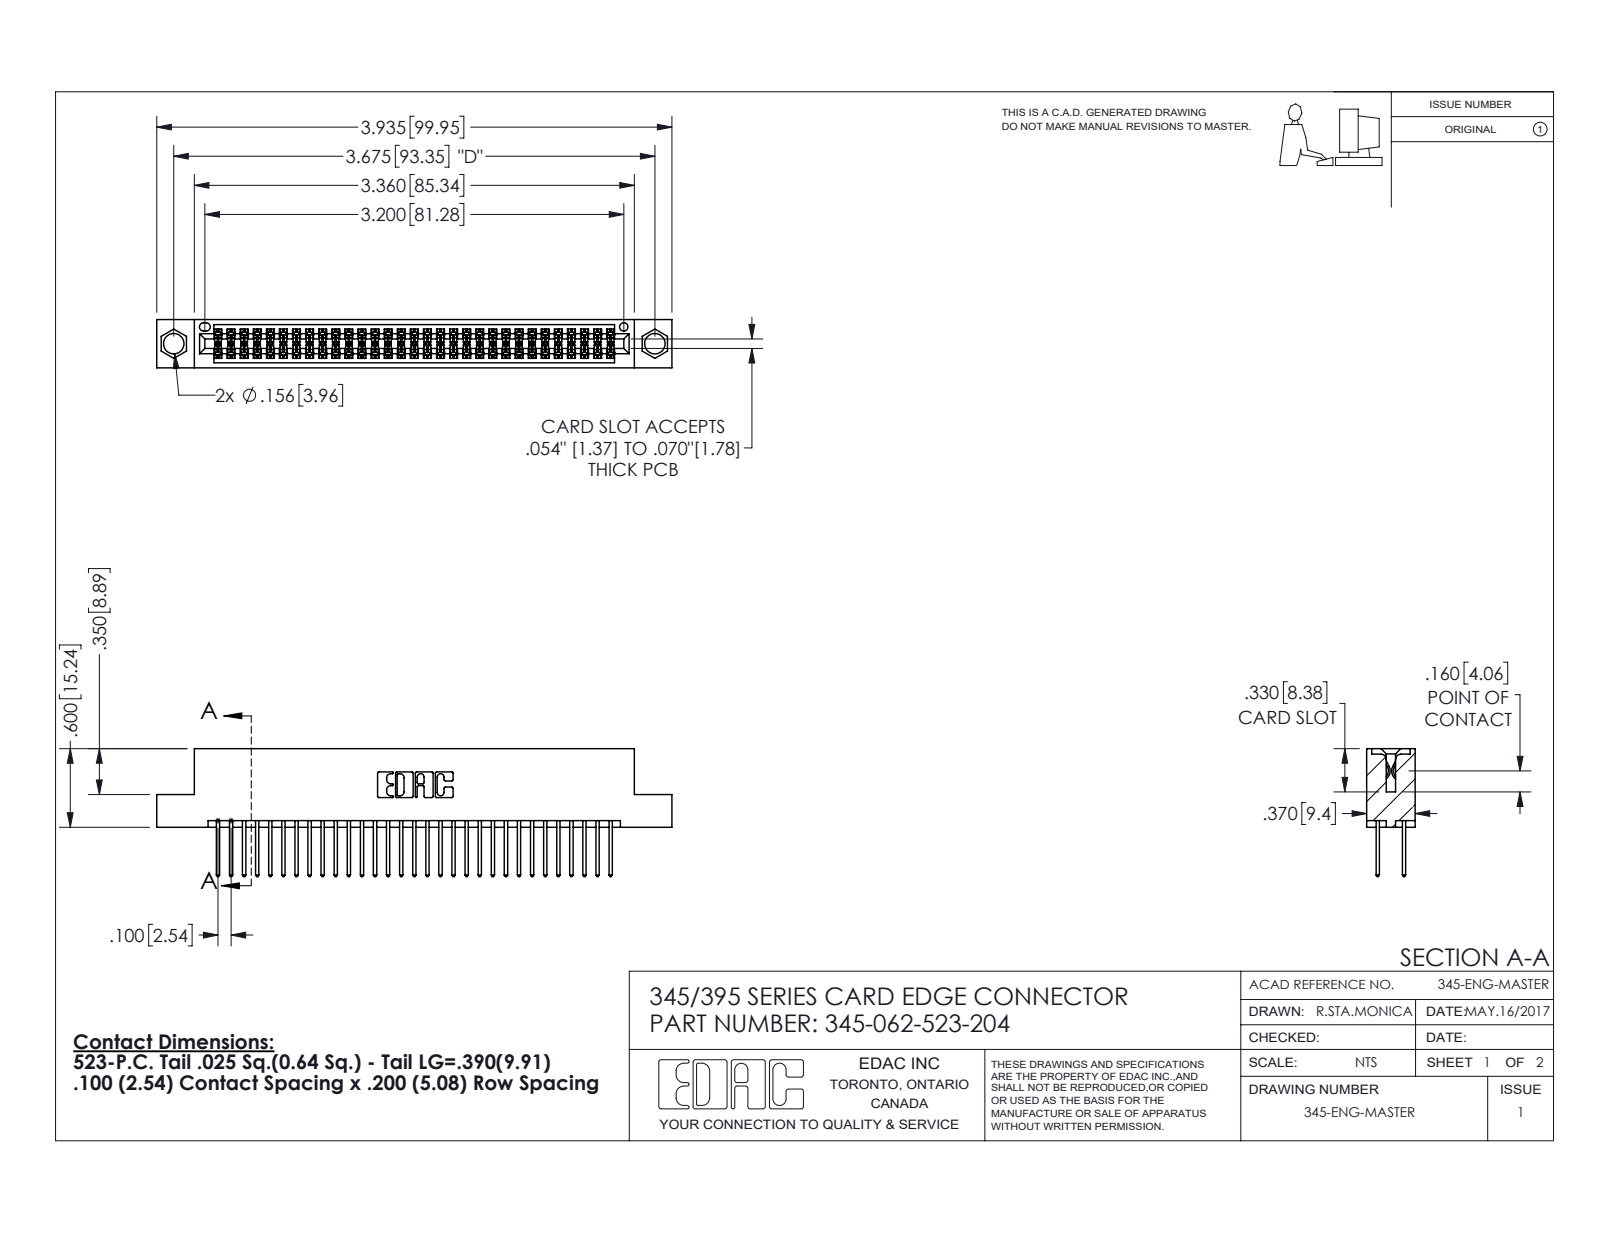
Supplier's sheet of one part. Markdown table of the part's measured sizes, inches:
| quantity | value |
| --- | --- |
| part name | 345-292-001_345-293-123; 345-062-523-204; 345 Part_Flush Mounting Lugs - 0.156 Dia-TI |
| STEP written by | SolidWorks 2020 (CONFIG_CONTROL_DESIGN) |
| units | inches |
| bodies | 63 solids, 3240 faces (2140 planar, 1100 cylindrical, 0 other) |
| overall size | 3.935 × 0.977 × 0.37 |
| volume | 0.588 in³ |
| surface area | 22.38 in² |
| round holes (diameter × count) | 0.156 × 2, 0.064 × 1 |
| partial cylindrical surfaces (radius × count) | 0.006 × 93, 0.01 × 62, 0.01 × 22, 0.007 × 6, 0.031 × 6, 0.026 × 3, 0.014 × 2, 0.019 × 2 |
| main face-to-face distances | 0.072, 0.298, 0.2, 0.098, 0.272, 0.025, 0.37, 0.225, 0.175, 0.149 |
| hole center spacings | 0.27, 3.44, 3.675 |
